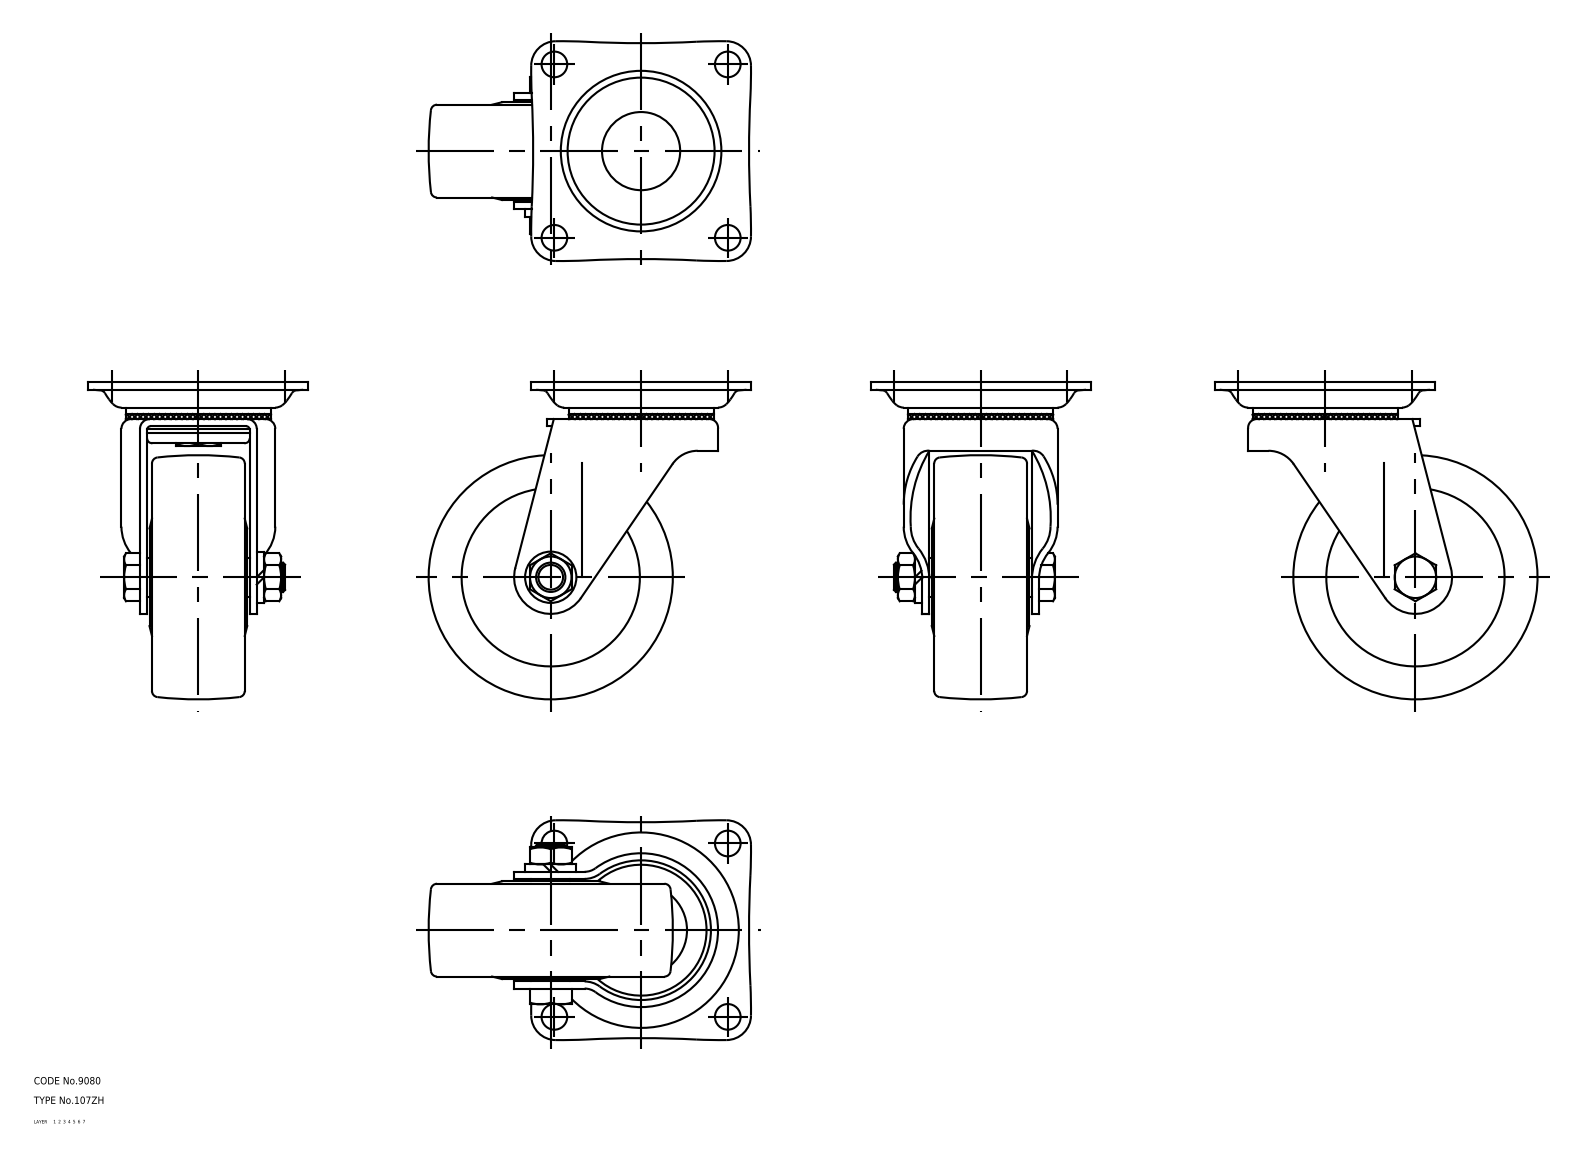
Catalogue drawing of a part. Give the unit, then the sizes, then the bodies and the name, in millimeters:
Units: millimetres
Overall size (bounding box): 132 × 130 × 90
Volume: 393 561 mm³ · Surface area: 79 986 mm²
Bodies: 5 solids, 217 faces (0 planar, 0 cylindrical, 217 other)
Part name (STEP PRODUCT): 67123441; 67123454; 67123467; 67123480 (+1 more)
STEP written by: CADfix (AUTOMOTIVE_DESIGN)
